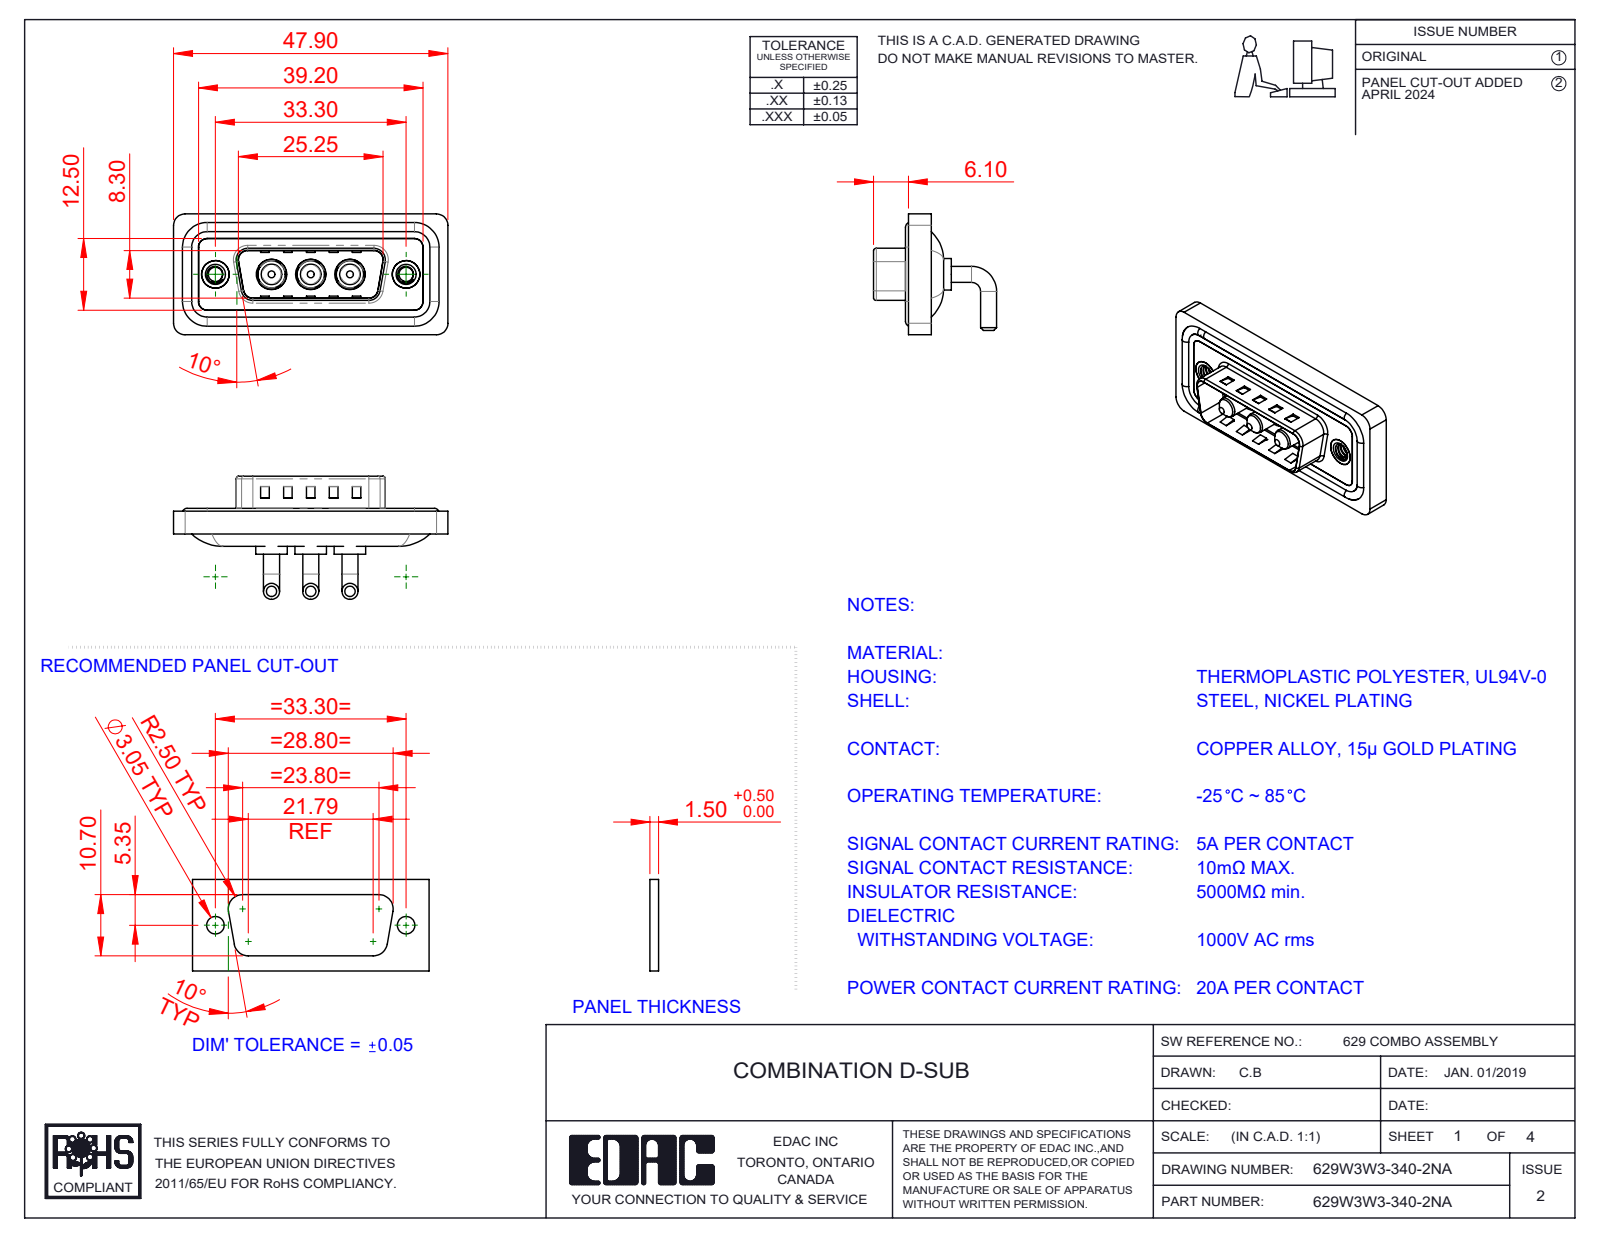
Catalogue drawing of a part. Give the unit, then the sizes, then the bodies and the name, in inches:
Units: inches
Overall size (bounding box): 1.886 × 0.846 × 0.831
Round holes (diameter × count): ⌀0.191 ×3, ⌀0.209 ×3, ⌀0.098 ×2, ⌀0.157 ×2, ⌀0.189 ×2, ⌀0.197 ×2
Round bosses / shafts (diameter × count): ⌀0.11 ×6, ⌀0.063 ×4, ⌀0.217 ×3, ⌀0.205 ×3, ⌀0.187 ×3, ⌀0.148 ×3, ⌀0.142 ×3, ⌀0.193 ×2
Partial cylindrical surfaces — rounded edges, fillets, slot ends (radius × count): R0.079 ×20, R0.059 ×18, R0.02 ×8, R0.063 ×8, R0.01 ×4, R0.024 ×4, R0.026 ×4, R0.035 ×4
Main face-to-face distances: 0.016, 0.114, 0.031, 0.043, 0.083, 0.063, 0.122, 0.098, 0.177, 0.146
Hole centre spacings: 0.27, 0.386, 0.656, 0.925, 0.539, 1.311
Volume: 0.353 in³ · Surface area: 14.01 in²
Bodies: 13 solids, 570 faces (207 planar, 245 cylindrical, 118 other)
Part name (STEP PRODUCT): 629Combo Housing_3W3; 629Combo Threaded Rivet_A; 629Combo Waterproof Housing_15 Contacts; 629Combo Shell Front_15 Contacts (+3 more)
STEP written by: SolidWorks 2023 (CONFIG_CONTROL_DESIGN)
